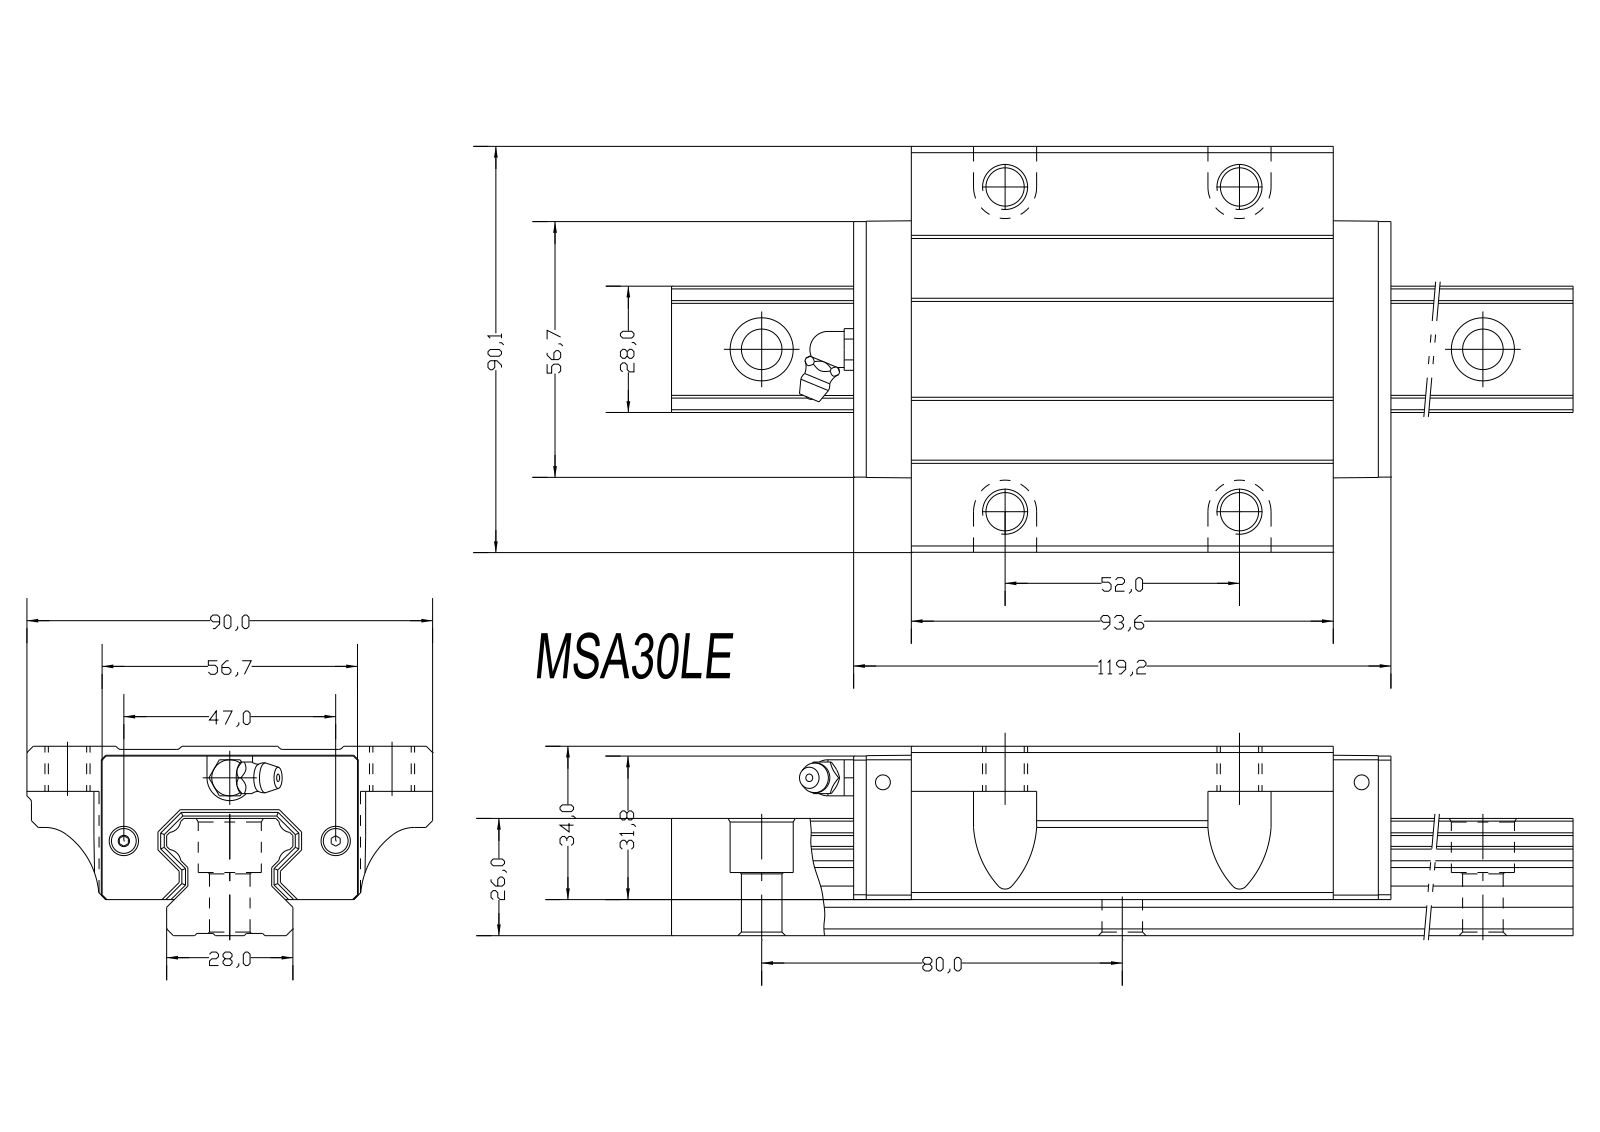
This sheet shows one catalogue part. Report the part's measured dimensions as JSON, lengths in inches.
{"step_written_by": "Kubotek KeyCreator V6.5.2 (0407) (CONFIG_CONTROL_DESIGN)", "units": "inches", "bodies": {"solids": 3, "faces": 258, "planar": 162, "cylindrical": 79, "other": 17}, "overall_size": [11.024, 3.543, 1.654], "volume_in3": 23.88, "surface_area_in2": 115.6, "round_holes": [[0.354, 4], [0.394, 4], [0.551, 4], [0.256, 3], [0.128, 2]], "round_bosses_or_shafts": [[0.315, 1]], "partial_cylinders_radius": [[0.122, 4], [0.276, 4], [0.315, 2], [0.709, 2], [0.039, 1], [0.199, 1]], "face_to_face_distances": [0.63, 0.709, 1.024, 1.654, 0.315, 1.339, 0.188, 0.915, 0.028, 1.626], "hole_center_spacings": [1.521, 2.96, 3.963, 5.92, 3.15, 1.077, 2.047, 2.835]}
